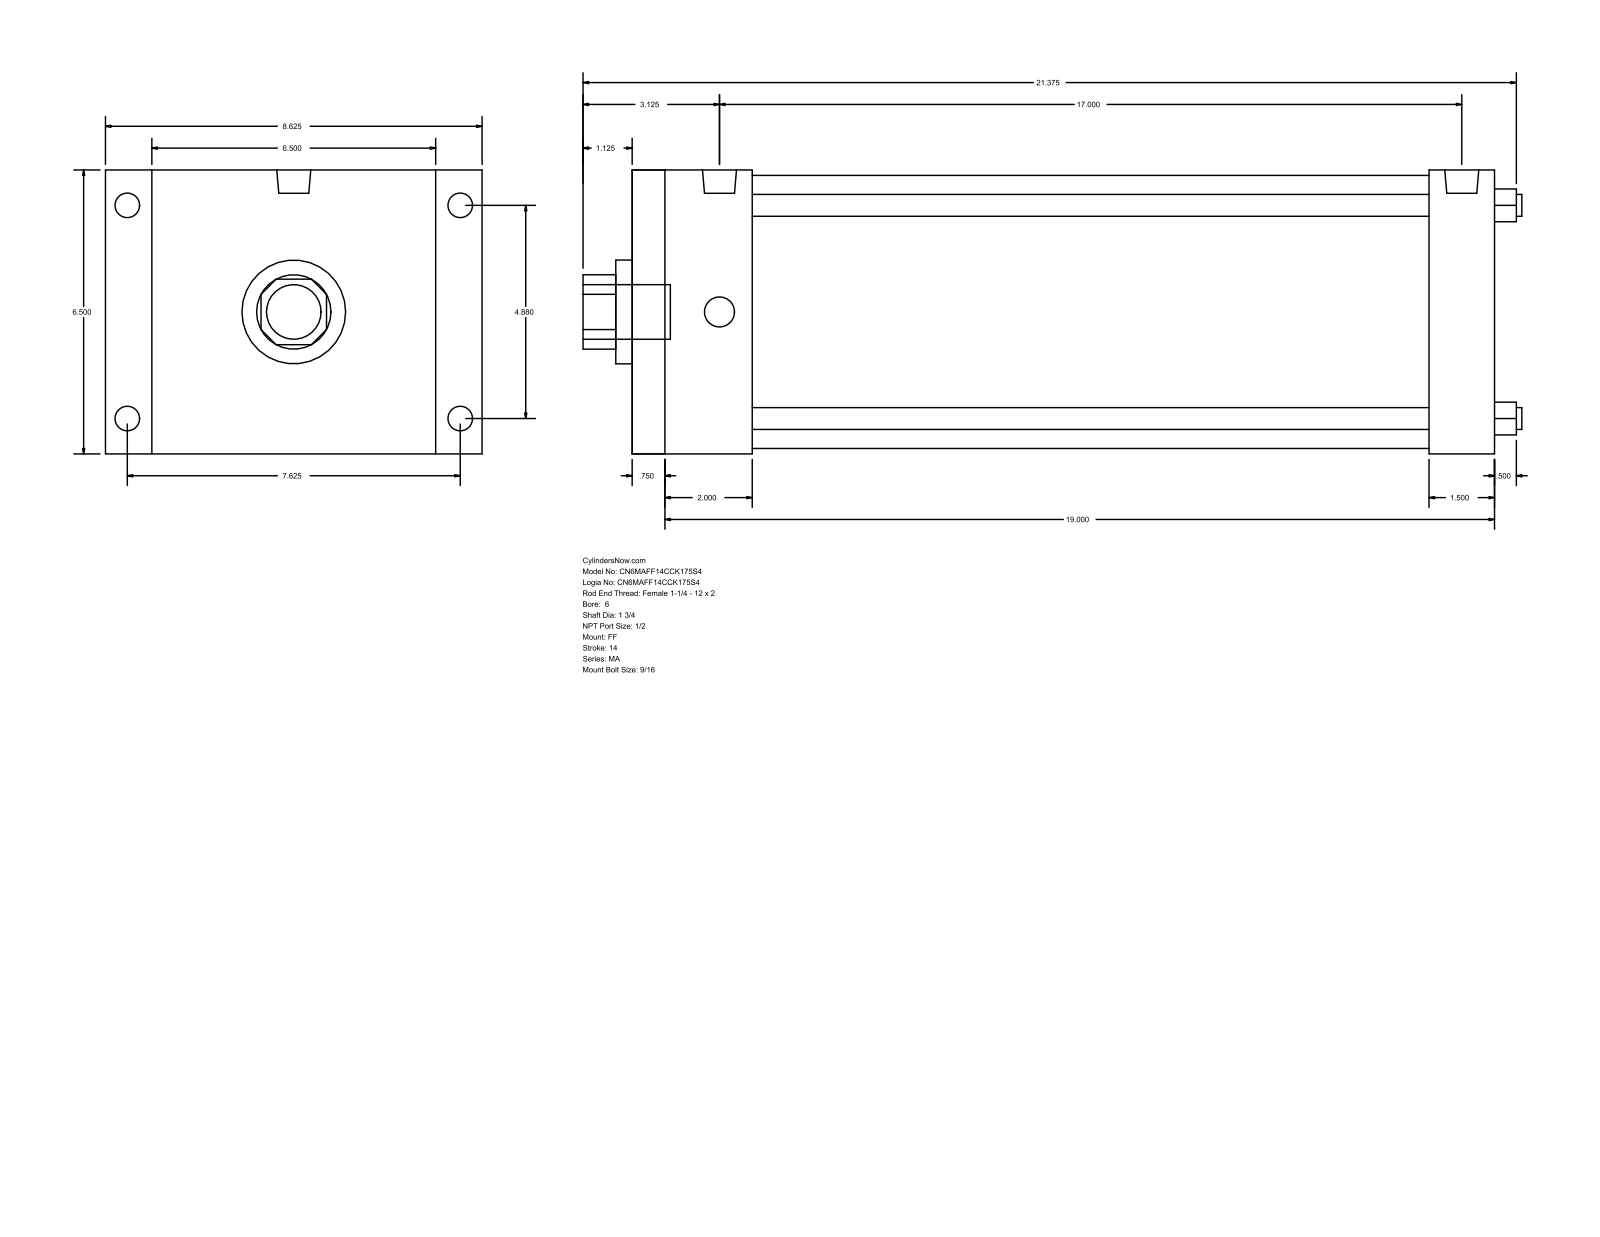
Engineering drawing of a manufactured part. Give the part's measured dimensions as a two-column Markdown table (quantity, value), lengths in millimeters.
| quantity | value |
| --- | --- |
| part name | MA_FF__0600_1.75 |
| STEP written by | GSSL Pune (CONFIG_CONTROL_DESIGN) |
| units | millimeters |
| bodies | 0 solids, 92 faces (64 planar, 28 cylindrical, 0 other) |
| overall size | 546.1 × 219.07 × 165.1 |
| round holes (diameter × count) | 12.7 × 4, 44.45 × 1, 60.33 × 1, 158.75 × 1 |
| round bosses / shafts (diameter × count) | 17.46 × 4, 14.29 × 4, 19.77 × 2, 31.75 × 1 |
| partial cylindrical surfaces (radius × count) | 21.63 × 1 |
| main face-to-face distances | 165.1, 501.66, 19.05, 482.61, 50.8, 444.5, 69.85, 431.81, 463.55, 393.7 |
| hole center spacings | 87.65, 123.96, 175.31 |
